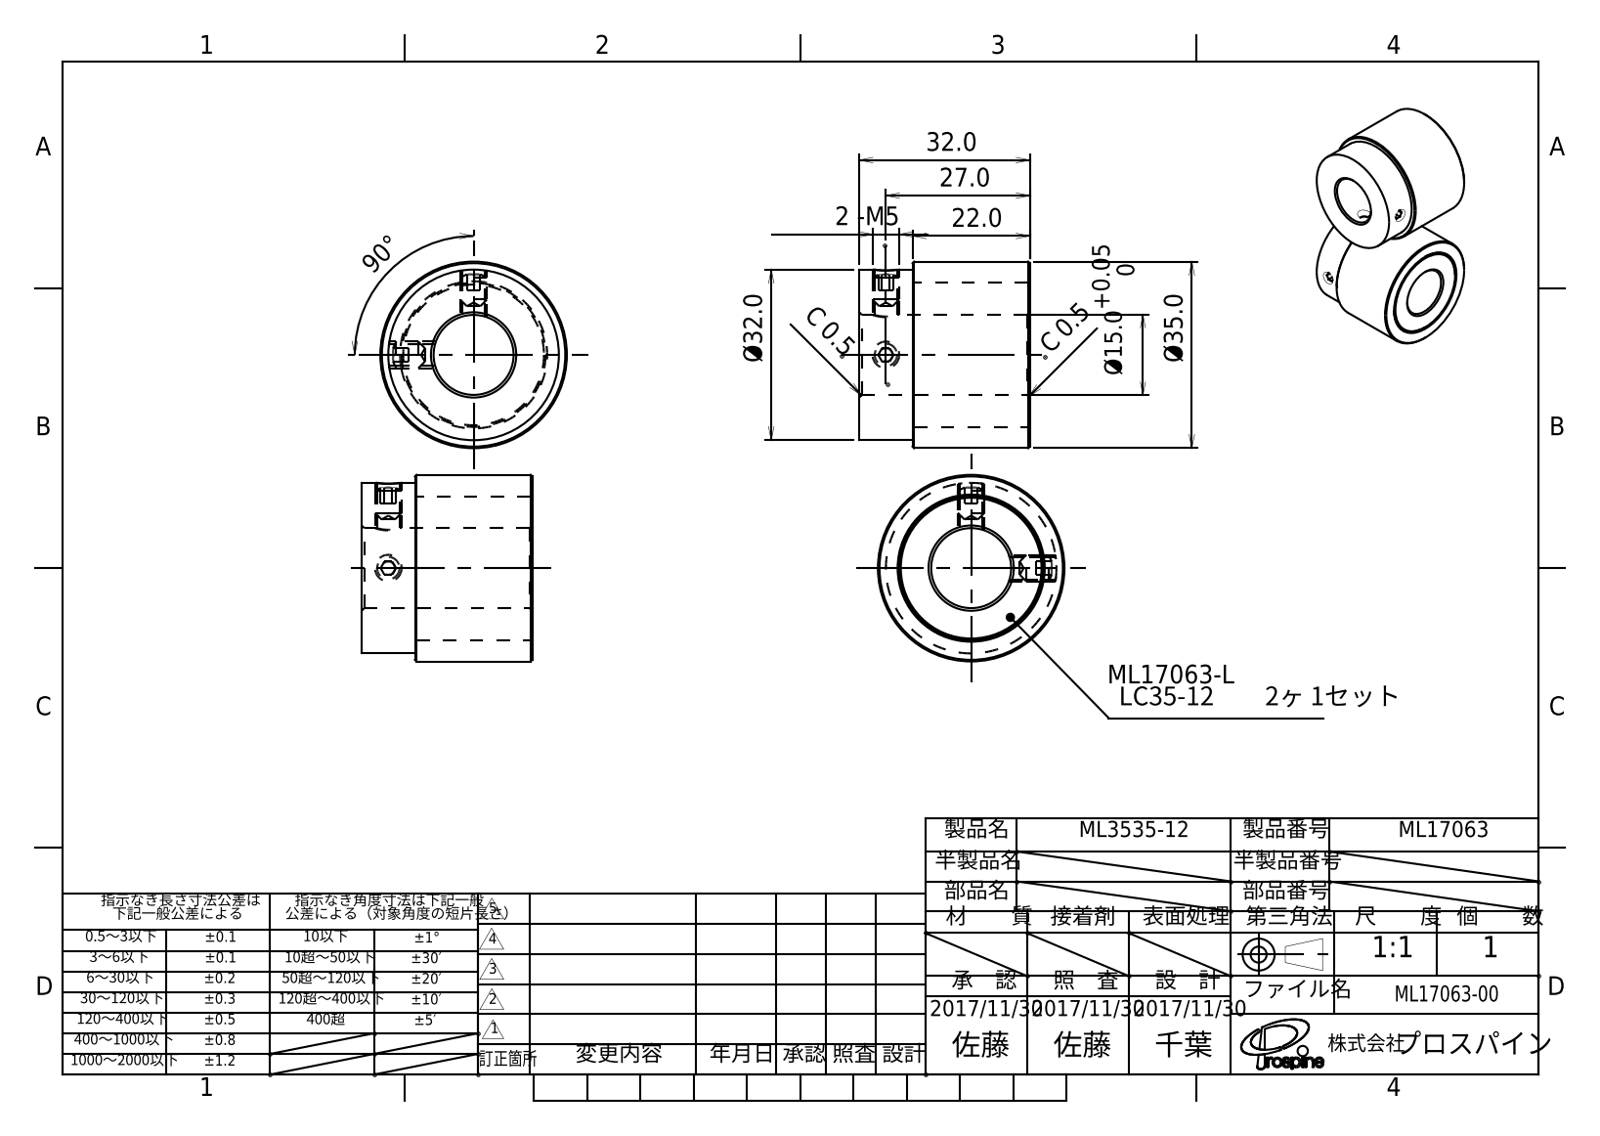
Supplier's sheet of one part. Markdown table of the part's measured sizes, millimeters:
| quantity | value |
| --- | --- |
| STEP written by | PSStep 10.0 (CONFIG_CONTROL_DESIGN) |
| units | millimeters |
| bodies | 9 solids, 93 faces (45 planar, 19 cylindrical, 29 other) |
| overall size | 75 × 38.5 × 38.5 |
| volume | 46 994 mm³ |
| surface area | 22 209 mm² |
| round holes (diameter × count) | 4.2 × 4, 15 × 2, 27 × 2 |
| round bosses / shafts (diameter × count) | 5 × 4, 35 × 2, 32 × 2 |
| main face-to-face distances | 32, 22, 10, 2.5, 9.75, 12.25, 10.88, 13.38, 40, 19.75 |
| hole center spacings | 43.08, 22.63 |
